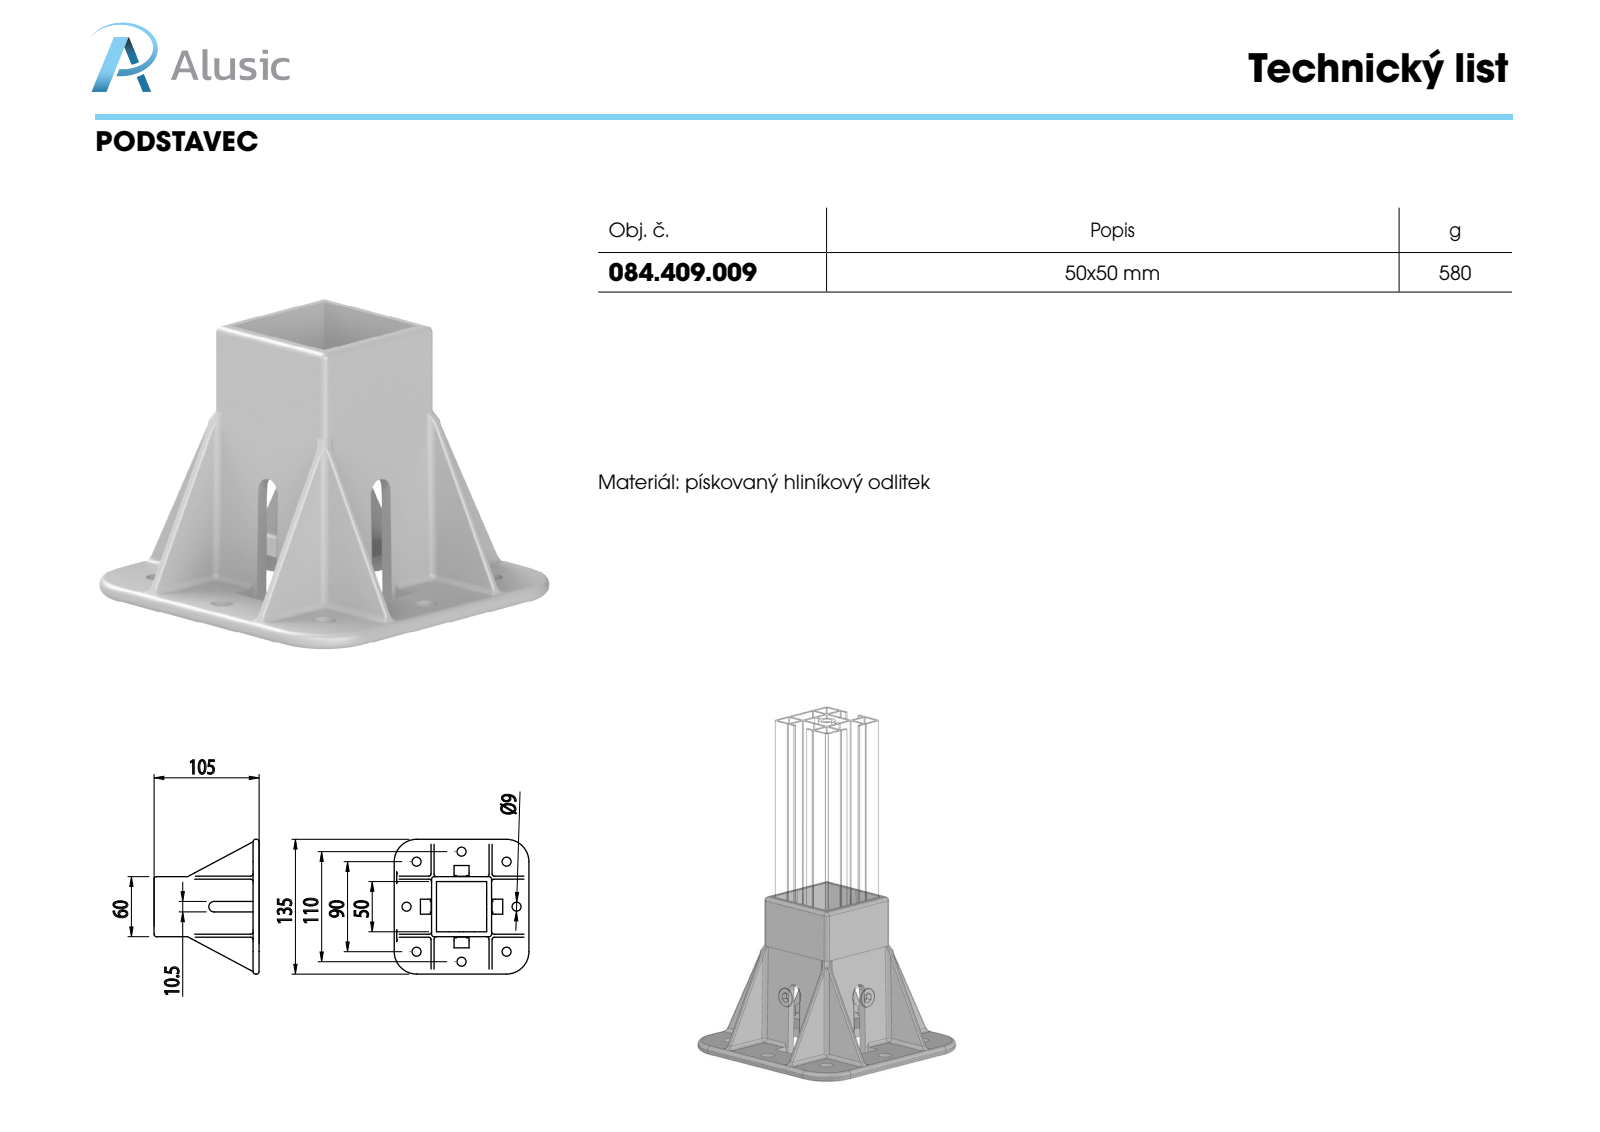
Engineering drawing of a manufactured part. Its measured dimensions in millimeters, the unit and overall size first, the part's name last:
Units: millimetres
Overall size (bounding box): 134.7 × 134.7 × 105
Round holes (diameter × count): ⌀9 ×8
Partial cylindrical surfaces — rounded edges, fillets, slot ends (radius × count): R2.5 ×48, R1 ×16, R22.5 ×4, R5.25 ×2
Main face-to-face distances: 6, 3, 58, 0.5, 60.5, 2.5, 57.5, 55, 61, 60
Hole centre spacings: 46.1, 109.66, 77.78, 90, 110, 127.28
Volume: 198 769 mm³ · Surface area: 93 760 mm²
Bodies: 1 solid, 302 faces (118 planar, 116 cylindrical, 68 other)
Part name (STEP PRODUCT): 084.409.009
STEP written by: SolidWorks 2012 (CONFIG_CONTROL_DESIGN)
